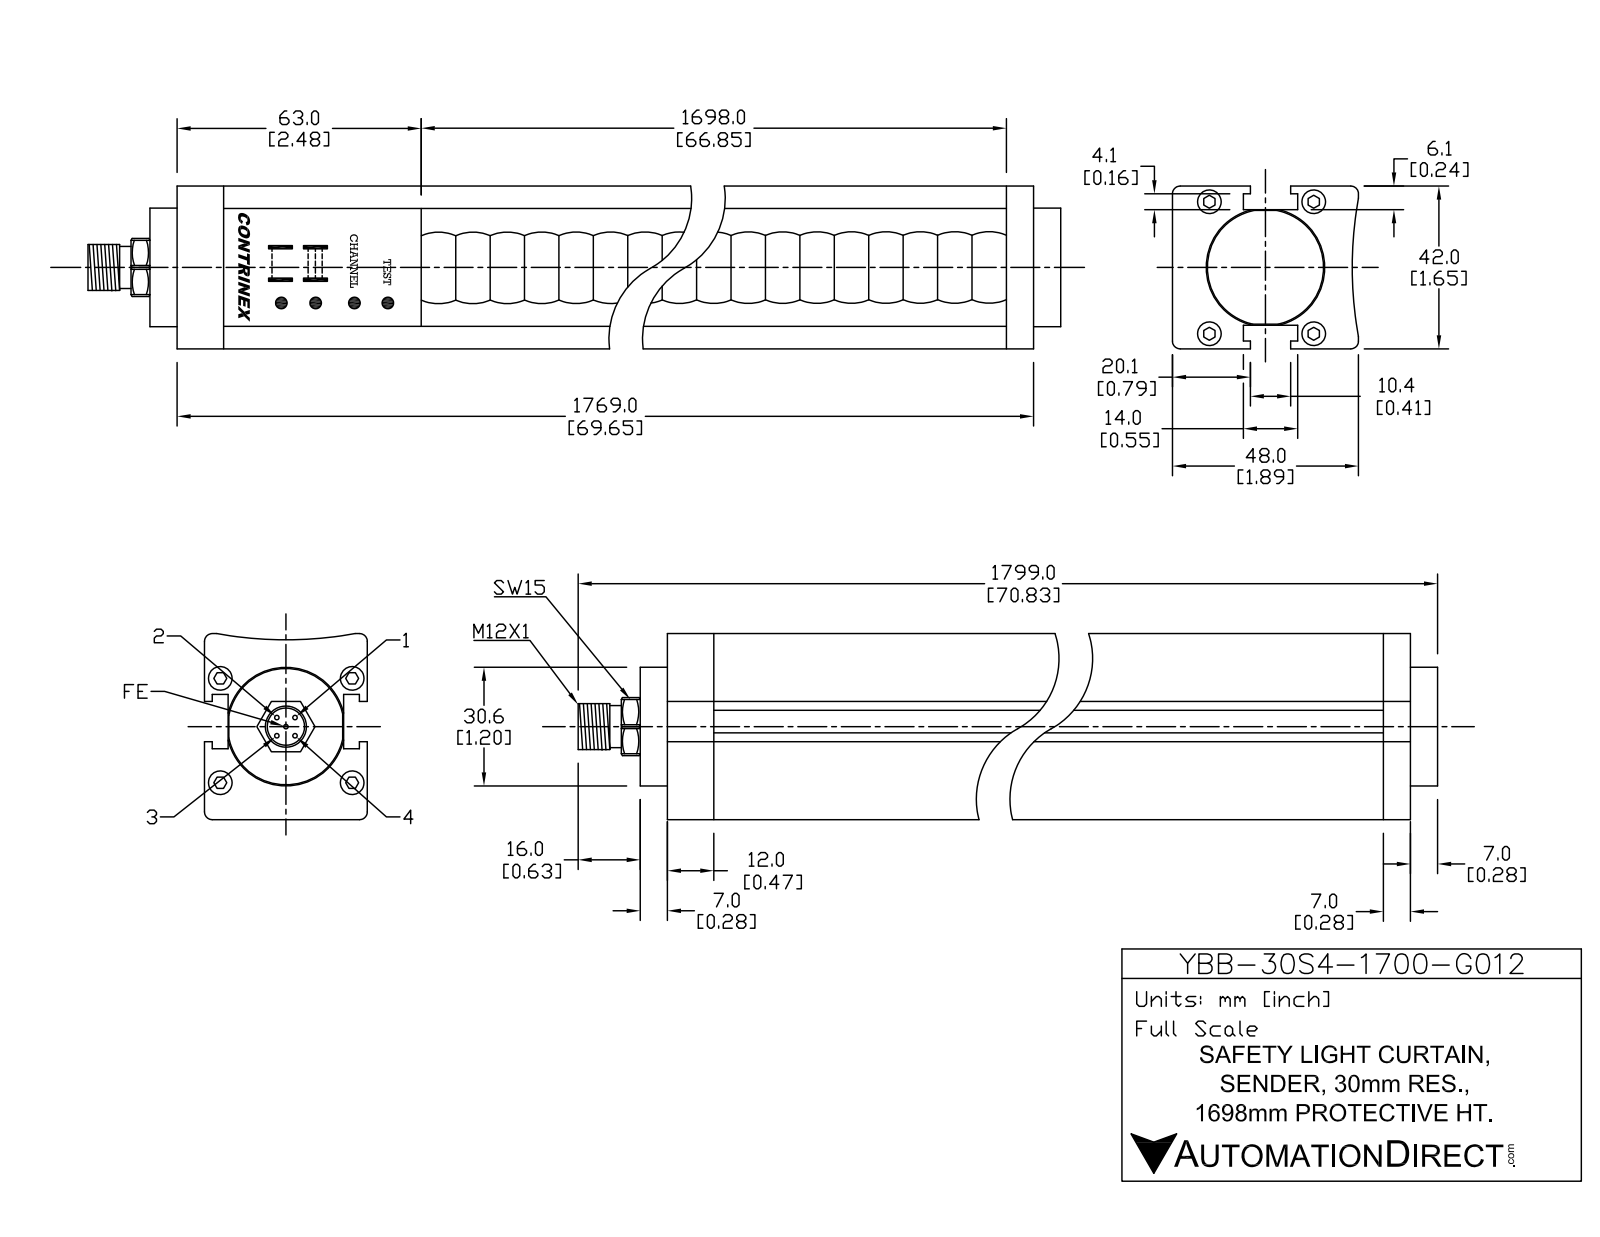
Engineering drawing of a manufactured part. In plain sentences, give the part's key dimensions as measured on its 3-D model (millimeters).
The part is named "YBB-30S4-1700-G012". Its 3-D file was written by "SolidWorks 2016 (AUTOMOTIVE_DESIGN)". It is 19 solids with 440 faces: 208 planar, 168 cylindrical and 64 other. Overall it measures 1799 by 48 by 42 millimeters. Its volume is 3 177 000 cubic millimeters and its surface area 394 749 square millimeters. Round holes: 4 of diameter 6, 1 of diameter 8.5, 1 of diameter 32. Round bosses or shafts: 5 of diameter 1, 4 of diameter 5.5, 1 of diameter 30.6, 1 of diameter 12, 1 of diameter 10.5. Partial cylindrical surfaces (rounded edges, fillets, slot ends): 48 of radius 1, 4 of radius 0.5, 2 of radius 0.55, 1 of radius 8.2, 1 of radius 100. The main face-to-face distances are 6.3, 35.7, 42, 29.4, 14, 17.2, 31.2, 15.7, 29.7, 46.9. The hole center spacings are 21.04, 22.34, 26.9, 34, 43.35.
